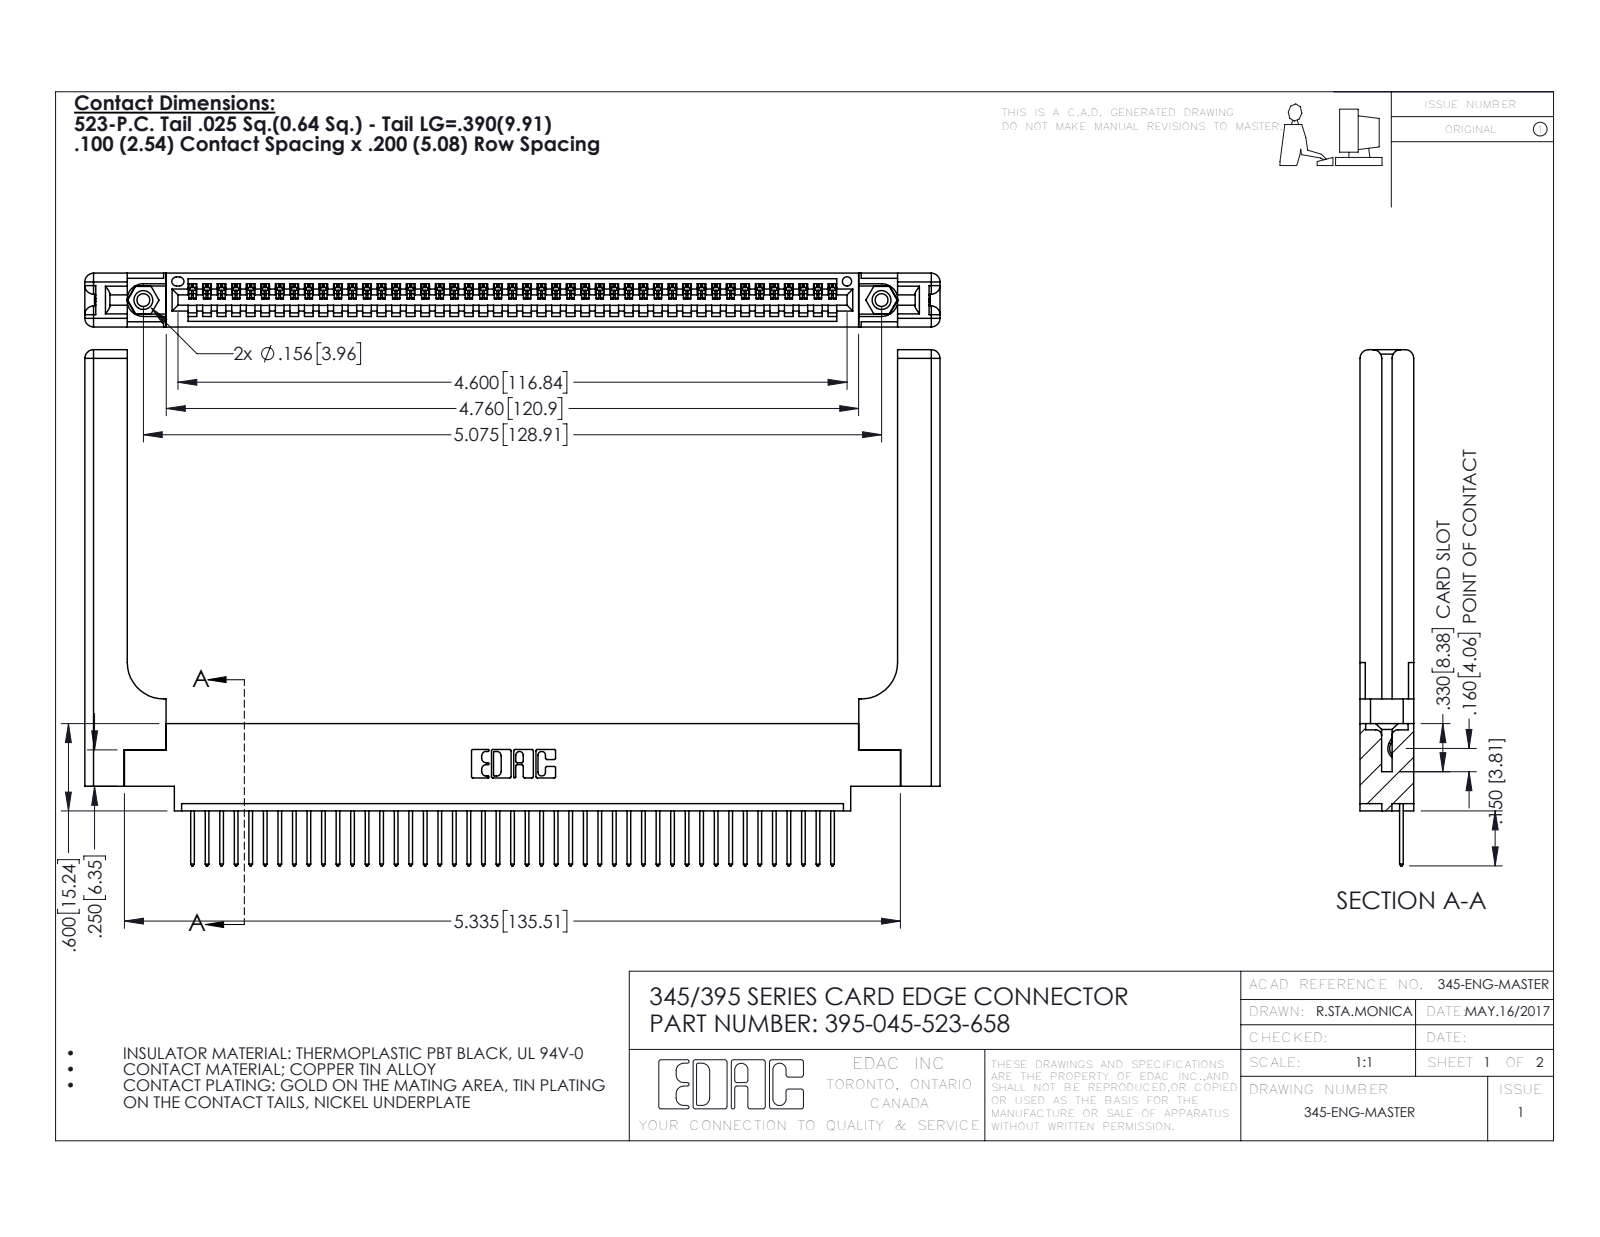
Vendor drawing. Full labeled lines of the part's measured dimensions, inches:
Part name (STEP PRODUCT): 345 Part_0.170 Offset - 0.156 Dia-TH; 345-220-058_345-220-058; 345-250-001_345-250-001-102; 345-292-001_345-293-123 (+1 more)
STEP written by: SolidWorks 2016 (CONFIG_CONTROL_DESIGN)
Units: inches
Bodies: 50 solids, 2996 faces (2032 planar, 904 cylindrical, 60 other)
Overall size (bounding box): 5.879 × 3.547 × 0.37
Volume: 1.378 in³ · Surface area: 37.55 in²
Round holes (diameter × count): ⌀0.089 ×2, ⌀0.125 ×2, ⌀0.156 ×2, ⌀0.064 ×1
Round bosses / shafts (diameter × count): ⌀0.155 ×2
Partial cylindrical surfaces — rounded edges, fillets, slot ends (radius × count): R0.006 ×90, R0.01 ×90, R0.01 ×22, R0.06 ×16, R0.007 ×6, R0.031 ×6, R0.026 ×3, R0.03 ×2
Main face-to-face distances: 0.37, 0.072, 0.298, 0.098, 0.272, 0.025, 0.2, 0.225, 0.148, 0.15
Hole centre spacings: 0.27, 4.839, 5.075
